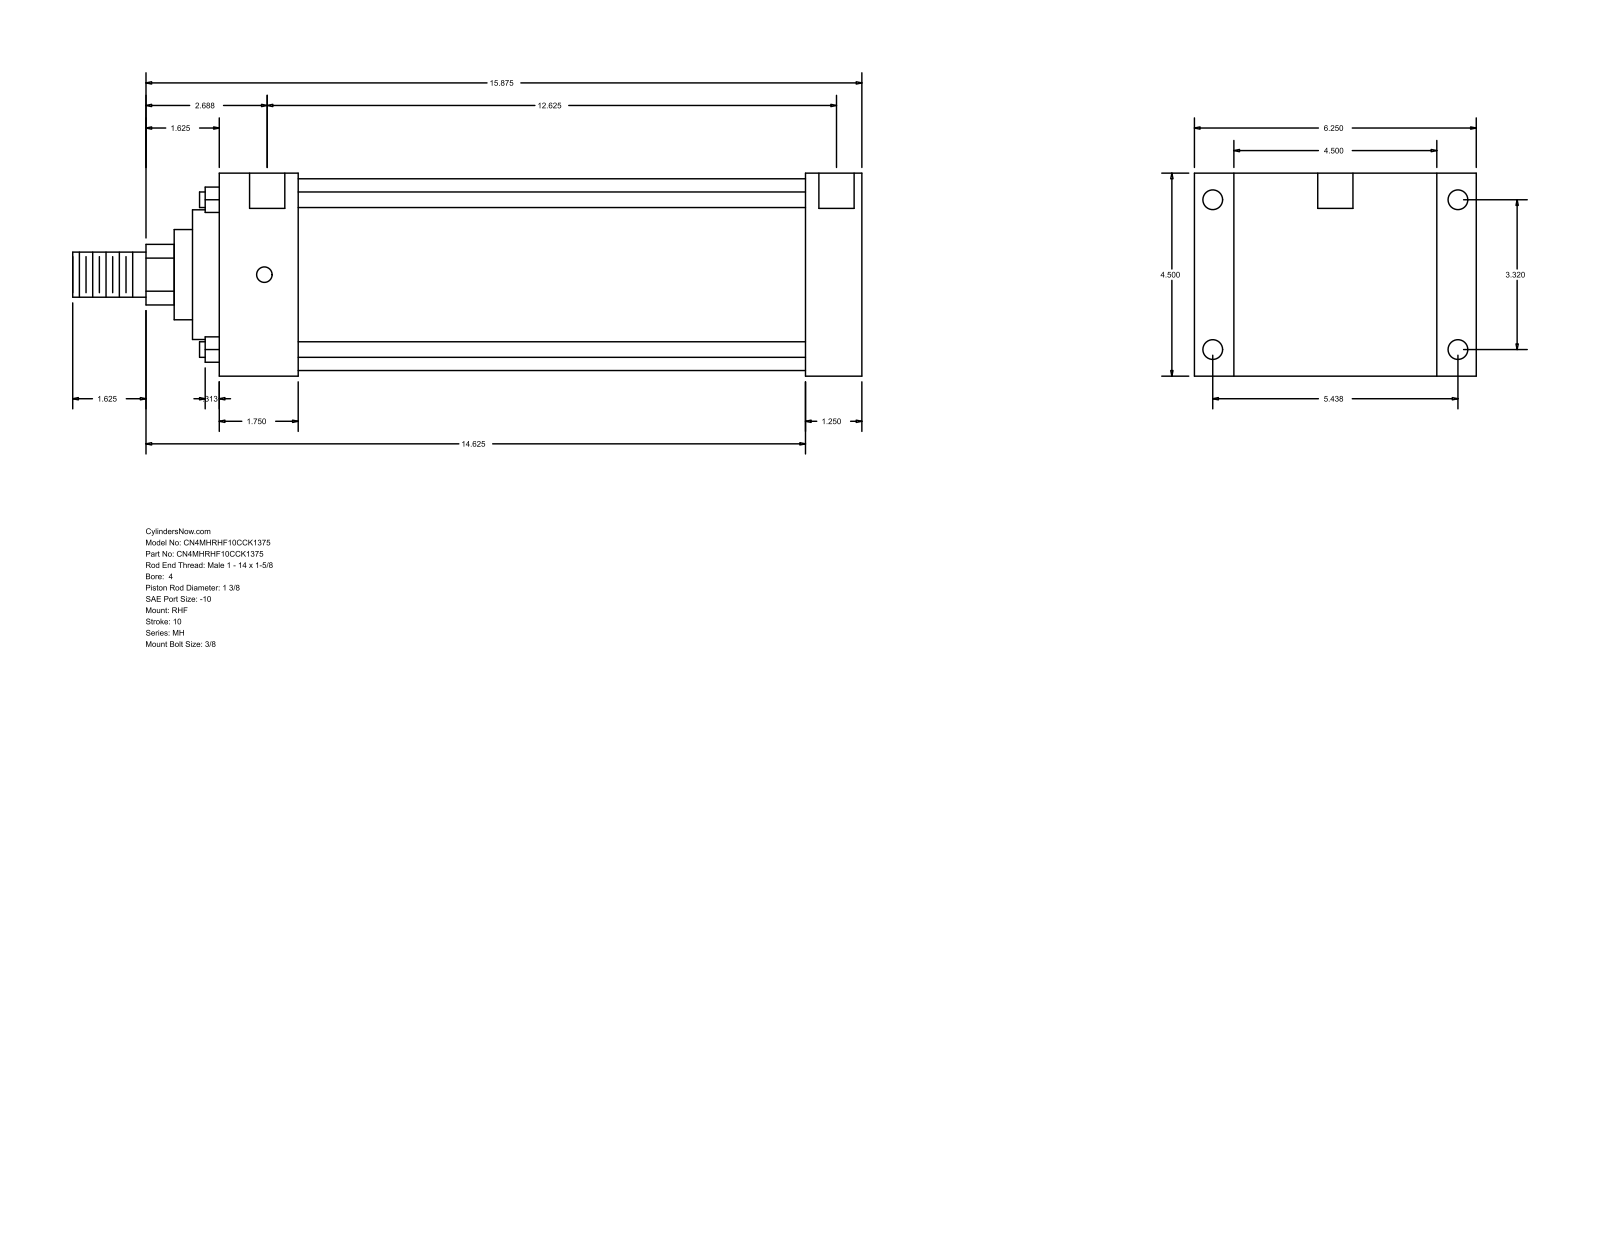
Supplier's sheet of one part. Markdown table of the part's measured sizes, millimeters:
| quantity | value |
| --- | --- |
| part name | MH_RHF__0400_1.375 |
| STEP written by | GSSL Pune (CONFIG_CONTROL_DESIGN) |
| units | millimeters |
| bodies | 0 solids, 90 faces (61 planar, 29 cylindrical, 0 other) |
| overall size | 444.5 × 158.75 × 114.3 |
| round holes (diameter × count) | 8.73 × 4, 11.13 × 4, 19.84 × 2 |
| round bosses / shafts (diameter × count) | 8.76 × 4, 107.95 × 1, 73.03 × 1, 50.8 × 1, 34.92 × 1, 25.4 × 1 |
| partial cylindrical surfaces (radius × count) | 17.06 × 1 |
| main face-to-face distances | 114.3, 31.75, 330.21, 361.96, 22.23, 136.53, 44.45, 285.76, 317.51, 158.76 |
| hole center spacings | 84.32, 138.12, 161.82, 323.85, 1.58, 1.59, 320.68, 322.26 |
